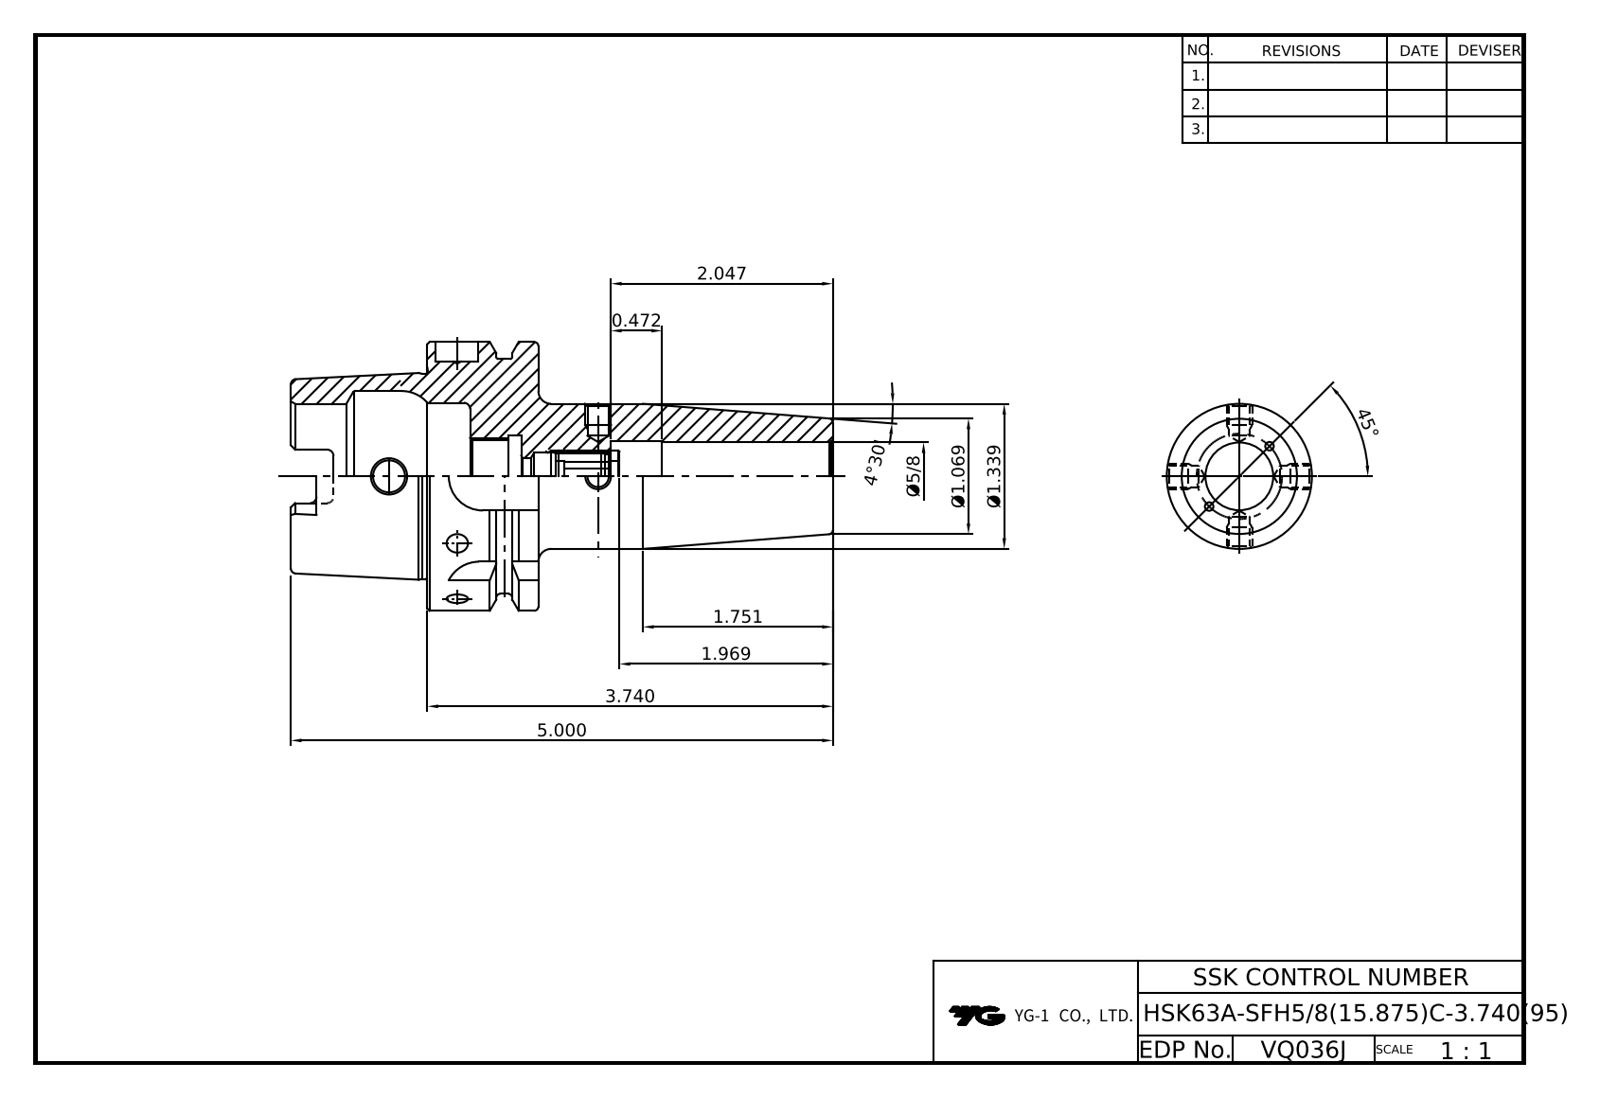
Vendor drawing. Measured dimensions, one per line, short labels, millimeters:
name: HSK63A_BALANCE_20200217
written by: CREO PARAMETRIC BY PTC INC, 2018500 (CONFIG_CONTROL_DESIGN)
unit: mm
bodies: 1 solid, 184 faces (57 planar, 57 cylindrical, 70 other)
size: 127 × 63 × 63
volume: 123 863 mm³; area: 33 335 mm²
holes: 2× ⌀5, 1× ⌀7.5, 1× ⌀8.4, 1× ⌀10, 1× ⌀11, 1× ⌀12, 1× ⌀15.88, 1× ⌀16.48, 1× ⌀17, 1× ⌀18, 1× ⌀19, 1× ⌀34
bosses: 1× ⌀63, 1× ⌀55, 1× ⌀48.04
rounds: 6× R1.5, 4× R2.88, 4× R8
face distances: 26, 10, 16, 32, 6.12, 9.88, 42, 58, 4, 69
